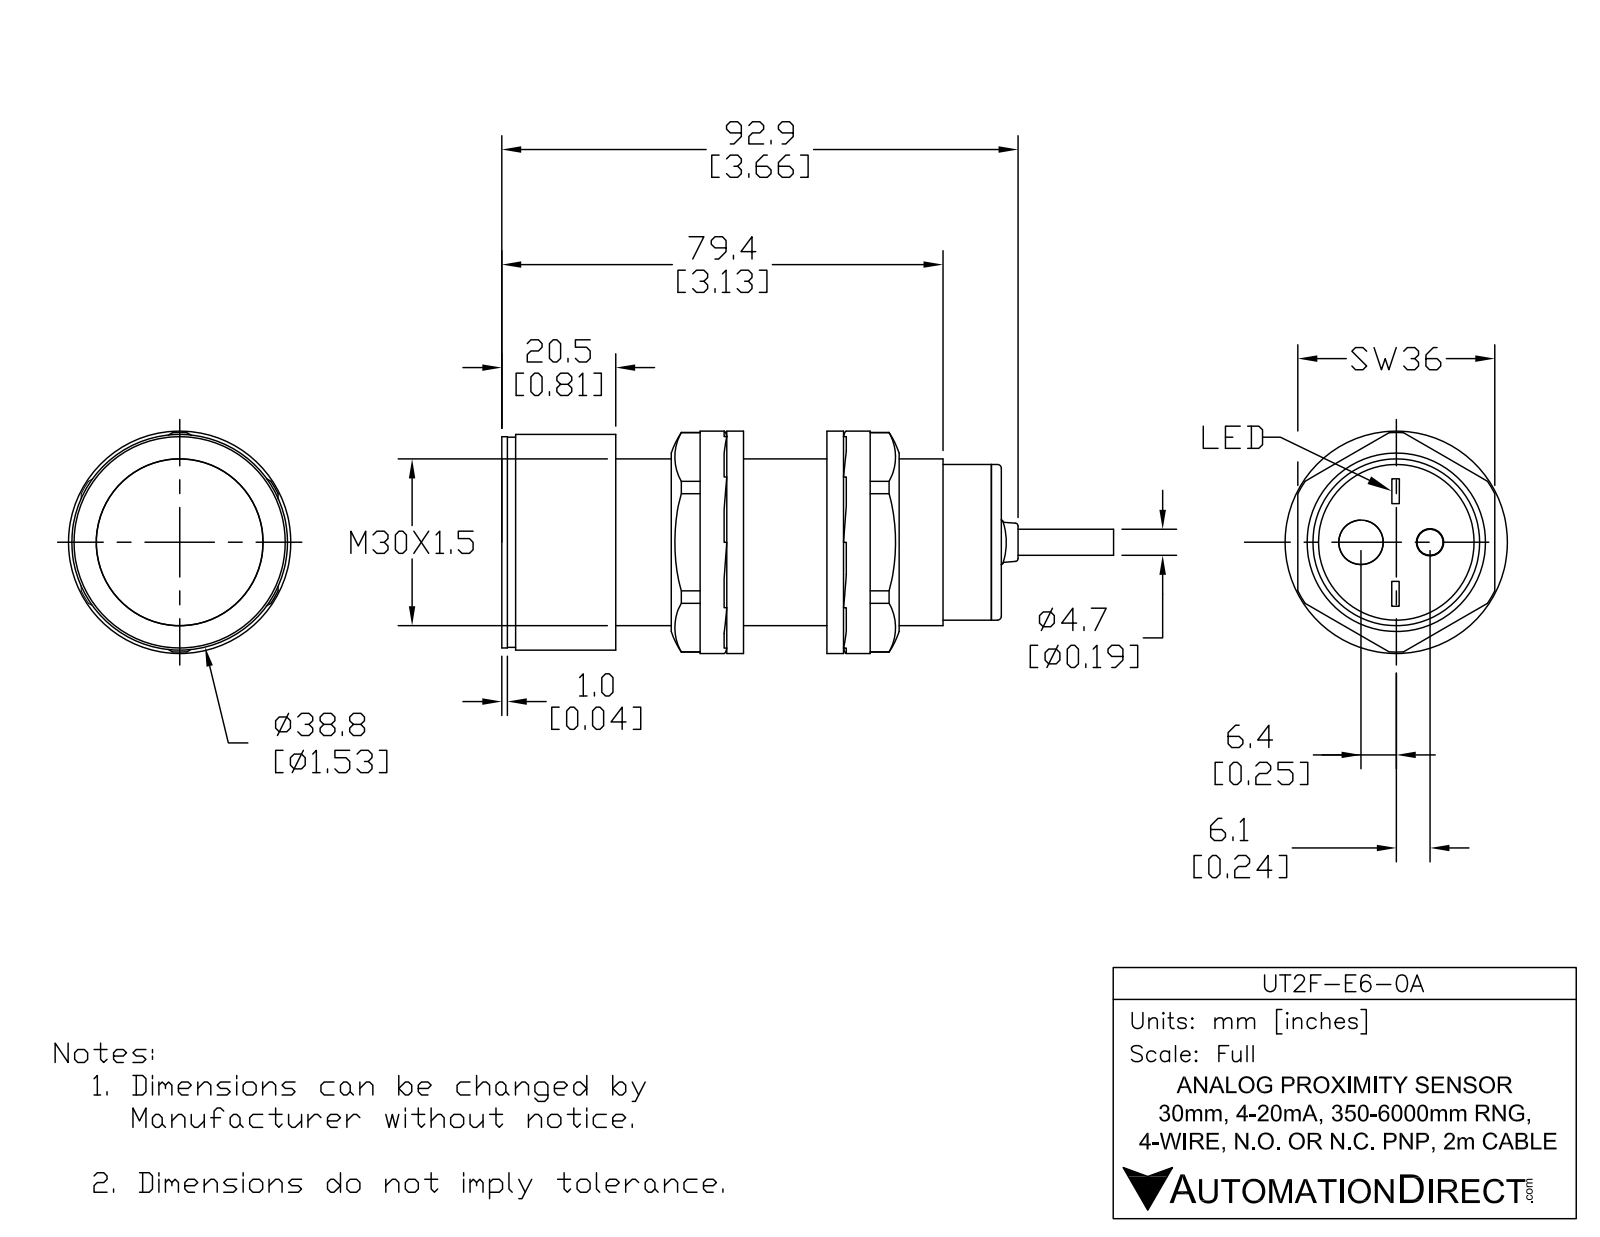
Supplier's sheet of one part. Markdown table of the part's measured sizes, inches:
| quantity | value |
| --- | --- |
| part name | UT2F-E6-0A |
| STEP written by | SolidWorks 2017 (AUTOMOTIVE_DESIGN) |
| units | inches |
| bodies | 5 solids, 49 faces (14 planar, 20 cylindrical, 15 other) |
| overall size | 5.043 × 1.528 × 1.528 |
| volume | 4.38 in³ |
| surface area | 24.02 in² |
| round holes (diameter × count) | 0.185 × 1, 0.315 × 1, 1.299 × 1 |
| round bosses / shafts (diameter × count) | 1.528 × 1, 1.488 × 1, 1.181 × 1, 1.102 × 1 |
| main face-to-face distances | 3.37, 0.059, 3.429, 0.767, 0.709, 2.661, 3.5, 3.441, 2.732, 0.071 |
| hole center spacings | 0.239, 0.25, 0.49 |
